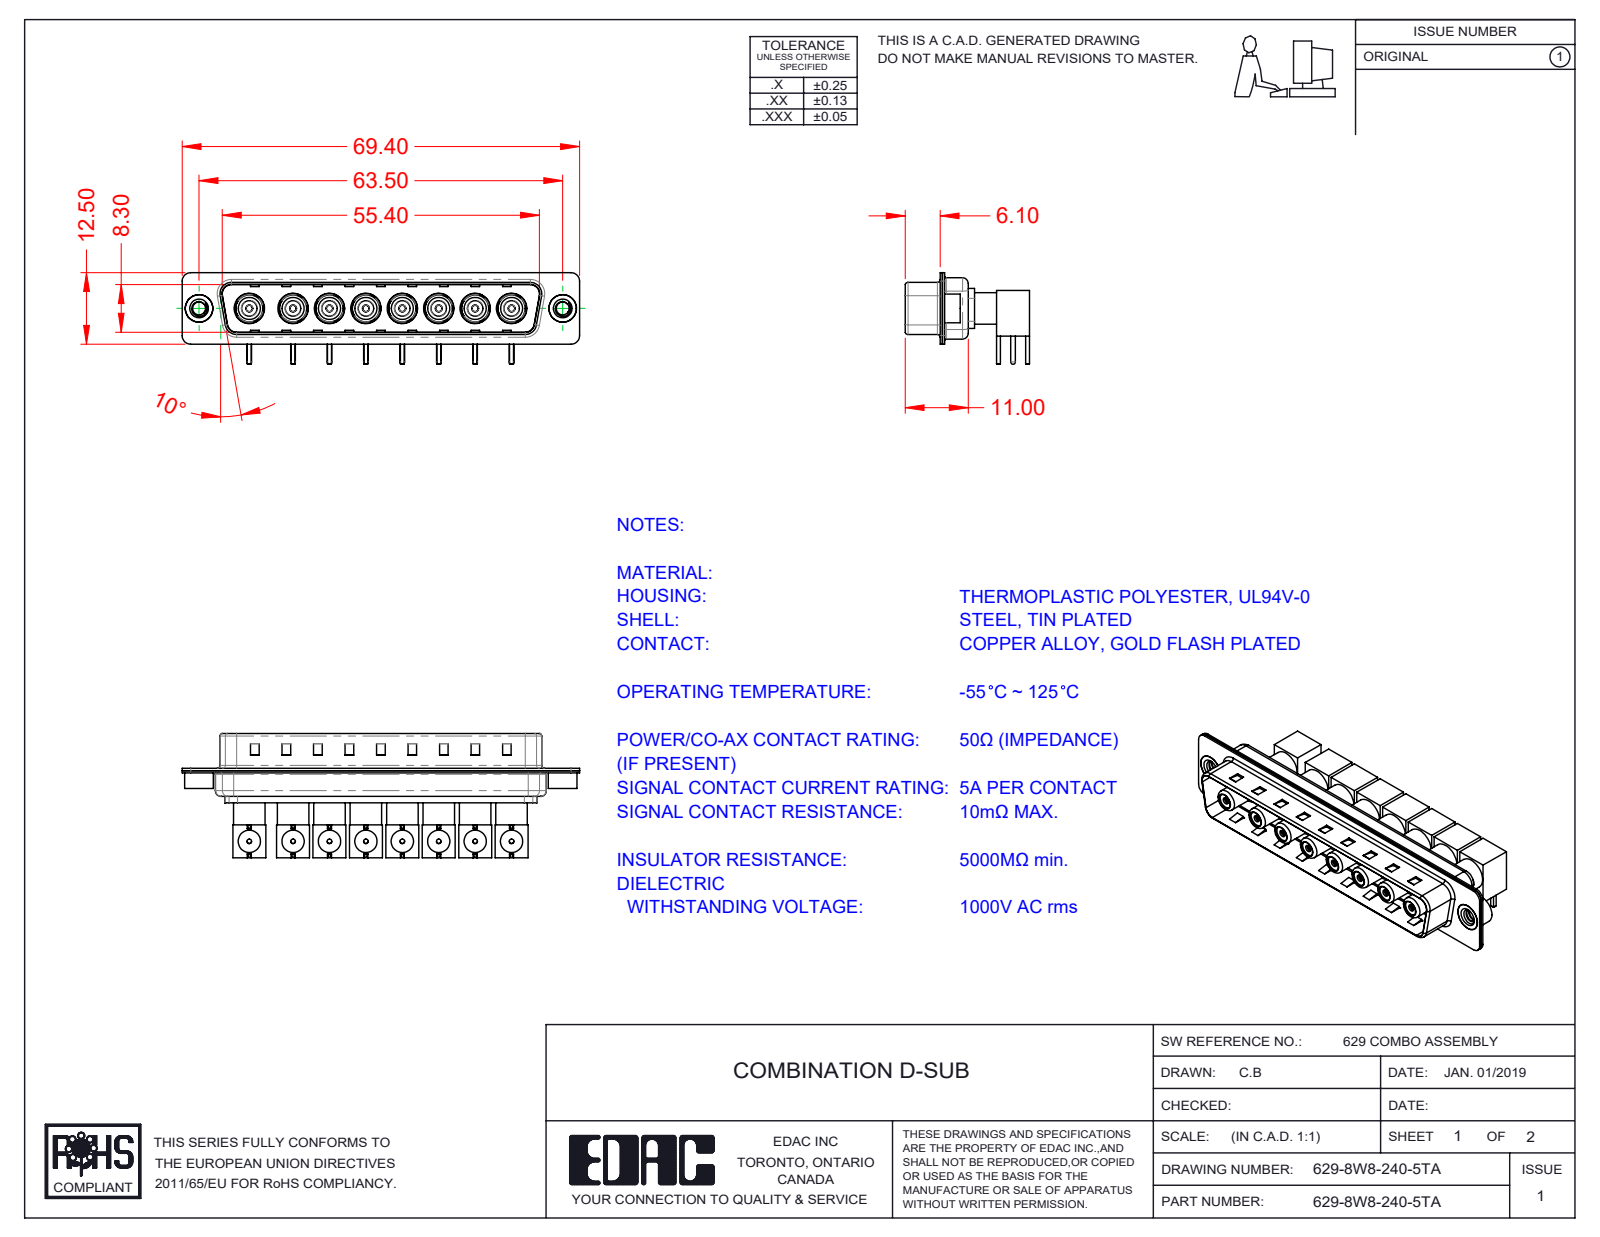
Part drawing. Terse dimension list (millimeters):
name: Co-Ax Jack_RA PC Tail; Co-Ax Jack Assy_RA; 629-8W8-240-5TA; 629Combo Housing_8W8 (+8 more)
written by: SolidWorks 2020 (CONFIG_CONTROL_DESIGN)
unit: mm
bodies: 61 solids, 1628 faces (659 planar, 677 cylindrical, 292 other)
size: 69.4 × 21.71 × 16
volume: 6 062 mm³; area: 16 755 mm²
holes: 8× ⌀0.8, 8× ⌀1.1, 8× ⌀1.2, 8× ⌀1.5, 8× ⌀1.6, 8× ⌀2.5, 8× ⌀2.7, 8× ⌀3.1, 8× ⌀3.4, 8× ⌀3.9, 8× ⌀4.1, 8× ⌀4.85
bosses: 16× ⌀0.8, 8× ⌀5.5, 8× ⌀5.2, 8× ⌀4.8, 8× ⌀4.73, 8× ⌀4.16, 8× ⌀4, 8× ⌀3.85
rounds: 16× R1.5, 12× R2, 8× R0.5, 8× R1.6, 8× R2.1, 4× R0.25, 4× R0.6, 4× R0.65
face distances: 0.4, 0.8, 9.5, 8.7, 9.1, 6.36, 5.75, 0.35, 1.4, 9.9
hole spacings: 6.36, 12.72, 19.08, 25.44, 31.8, 7.64, 14, 20.36
